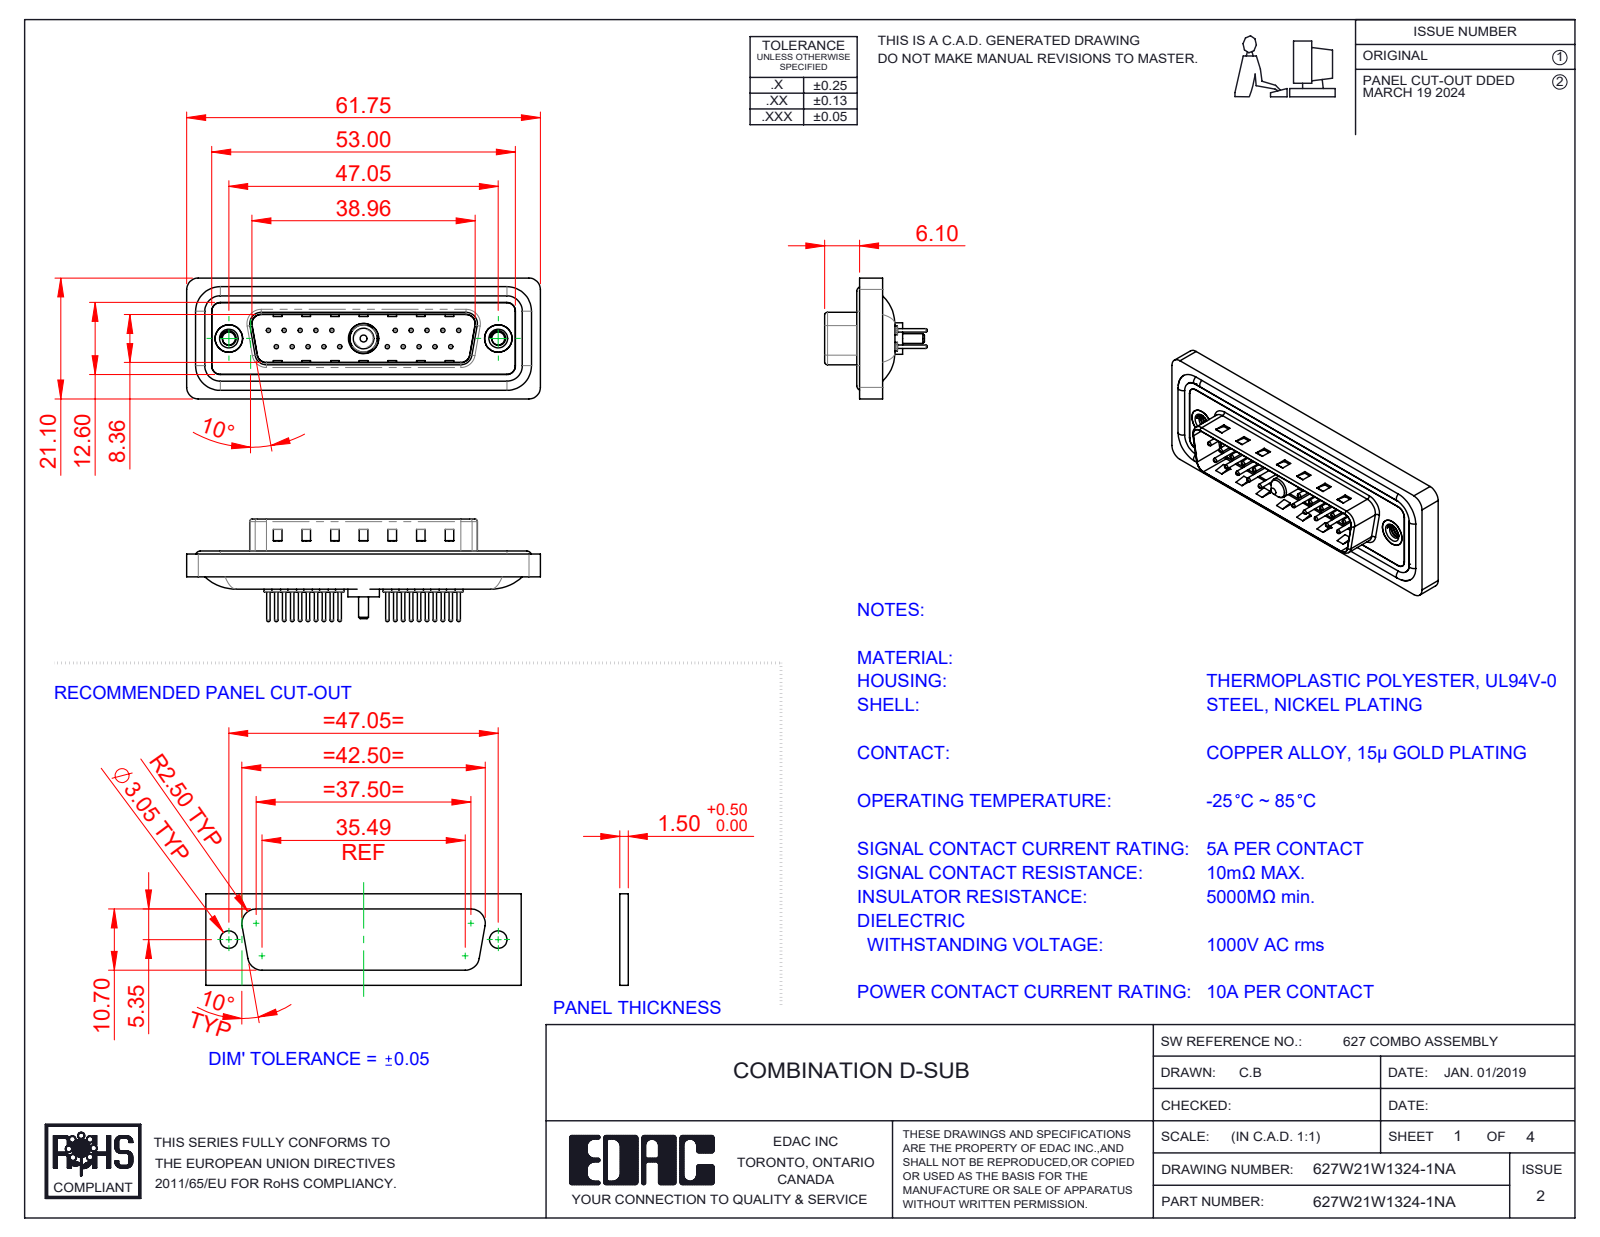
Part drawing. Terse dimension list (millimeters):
name: 627Combo Shell Rear_25 Contacts; 627Combo Threaded Rivet_A; 627Combo Shell Front_25 Contacts; 627Combo Housing_21W1 (+5 more)
written by: SolidWorks 2023 (CONFIG_CONTROL_DESIGN)
unit: mm
bodies: 29 solids, 1260 faces (359 planar, 489 cylindrical, 412 other)
size: 61.75 × 21.1 × 17.9
volume: 7 185 mm³; area: 11 938 mm²
holes: 20× ⌀0.75, 20× ⌀1.6, 20× ⌀2, 2× ⌀2.26, 2× ⌀4, 2× ⌀4.8, 2× ⌀5, 1× ⌀4.85, 1× ⌀5.3
bosses: 20× ⌀1.5, 20× ⌀0.6, 4× ⌀1.6, 2× ⌀4.9, 1× ⌀5.5, 1× ⌀5.2, 1× ⌀4.75, 1× ⌀3.75
rounds: 22× R1.5, 18× R2, 8× R0.5, 8× R1.6, 4× R0.25, 4× R0.6, 4× R0.65, 4× R0.9
face distances: 0.4, 1.5, 1.1, 1.6, 0.5, 3.1, 2.9, 4.1, 0.82, 9.58
hole spacings: 3.16, 2.77, 5.54, 8.31, 5.04, 19.39, 20.97, 22.16
